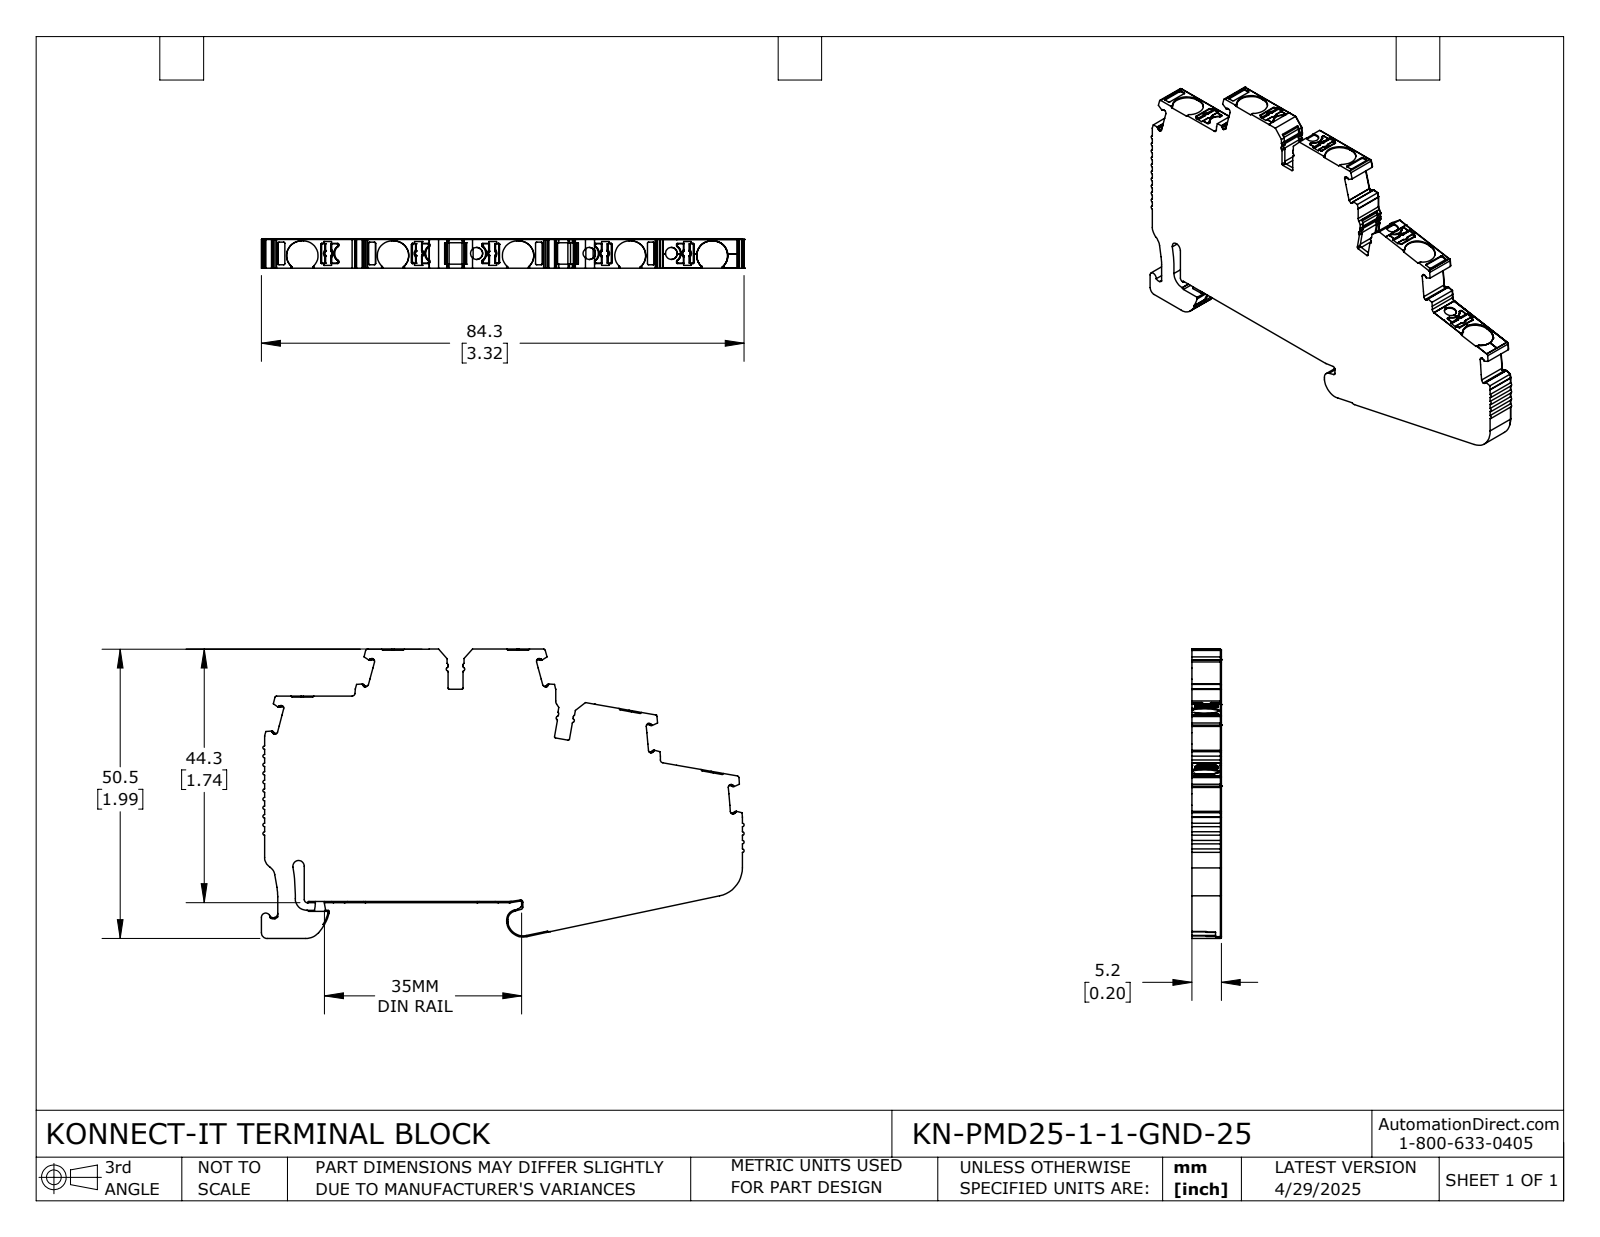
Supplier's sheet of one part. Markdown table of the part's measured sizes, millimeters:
| quantity | value |
| --- | --- |
| part name | KN-PMD25-1-1-GND-25 |
| STEP written by | SolidWorks 2024 (CONFIG_CONTROL_DESIGN) |
| units | millimeters |
| bodies | 1 solid, 1053 faces (524 planar, 444 cylindrical, 85 other) |
| overall size | 84.28 × 50.52 × 5.15 |
| volume | 15 779 mm³ |
| surface area | 7 993 mm² |
| round holes (diameter × count) | 2.1 × 3 |
| partial cylindrical surfaces (radius × count) | 0.2 × 92, 0.3 × 48, 0.1 × 33, 0.15 × 20, 0.5 × 19, 0.4 × 18, 0.6 × 12, 0.16 × 10 |
| main face-to-face distances | 5.15, 44.06, 35.87, 8.19, 44.05, 8.18, 2, 5, 6.26, 43.86 |
| hole center spacings | 15.95 |
